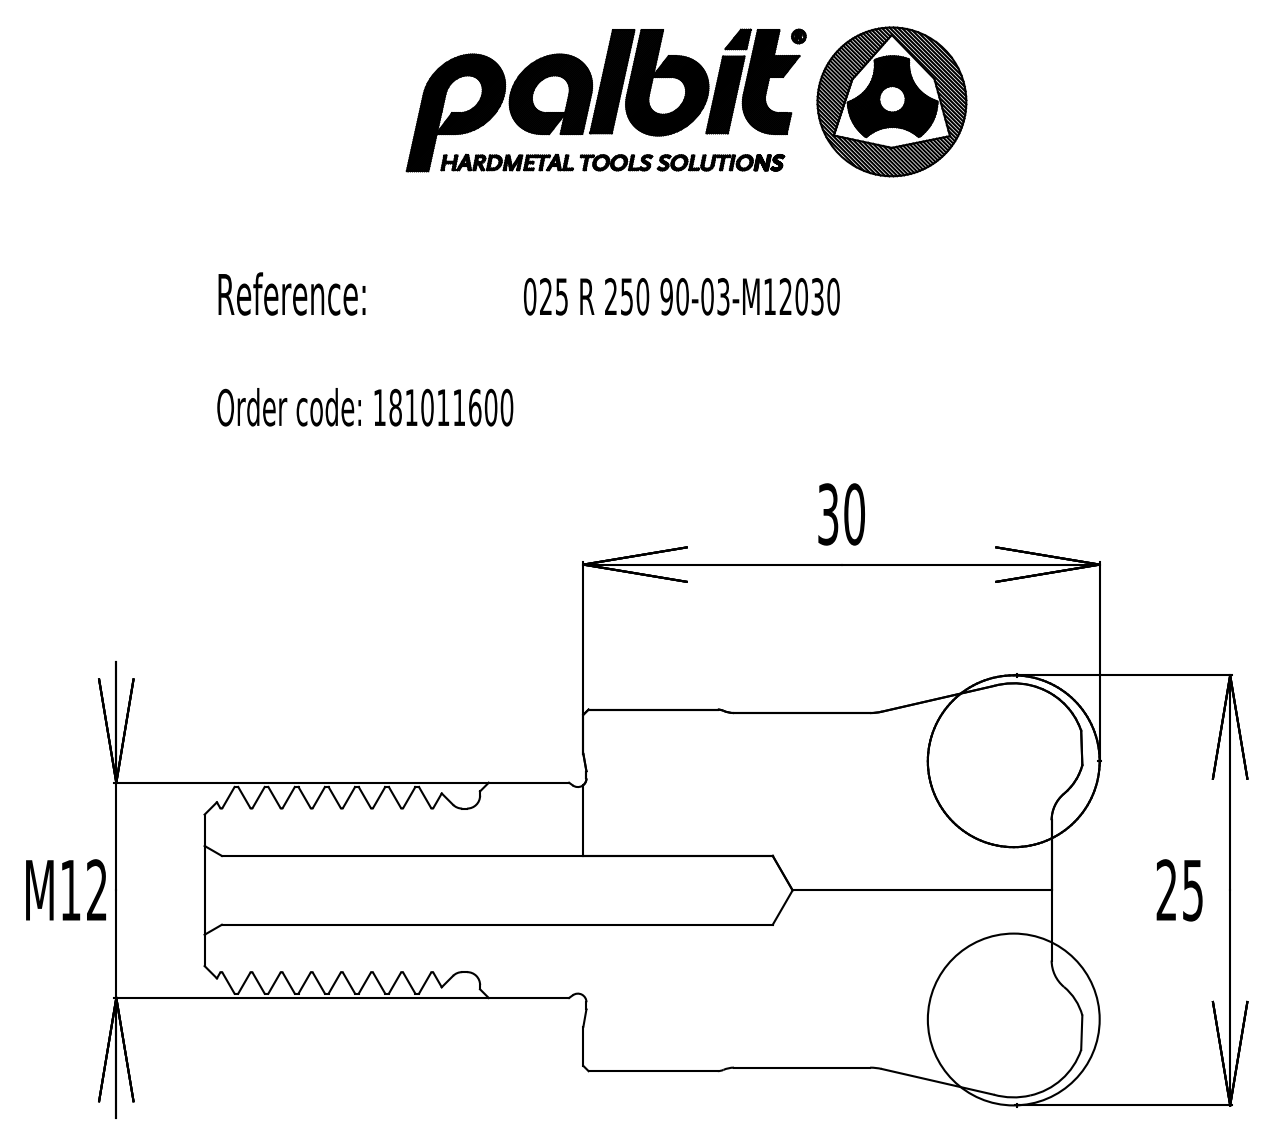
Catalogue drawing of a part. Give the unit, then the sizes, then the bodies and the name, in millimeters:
Units: millimetres
Overall size (bounding box): 51.99 × 24.98 × 24.98
Round holes (diameter × count): ⌀4 ×1
Round bosses / shafts (diameter × count): ⌀21 ×1, ⌀20.6 ×1, ⌀12.5 ×1, ⌀12 ×1, ⌀9.5 ×1
Main face-to-face distances: 27.2, 49.2, 22, 27.02, 22.18, 33.2, 6.18, 6, 16
Volume: 15 741 mm³ · Surface area: 5 688 mm²
Bodies: 2 solids, 64 faces (5 planar, 12 cylindrical, 47 other)
Part name (STEP PRODUCT): CUT PROFILE - 181011600; NOCUT^CUT PROFILE - 181011600; CUT^CUT PROFILE - 181011600
STEP written by: SolidWorks 2015 (CONFIG_CONTROL_DESIGN)
